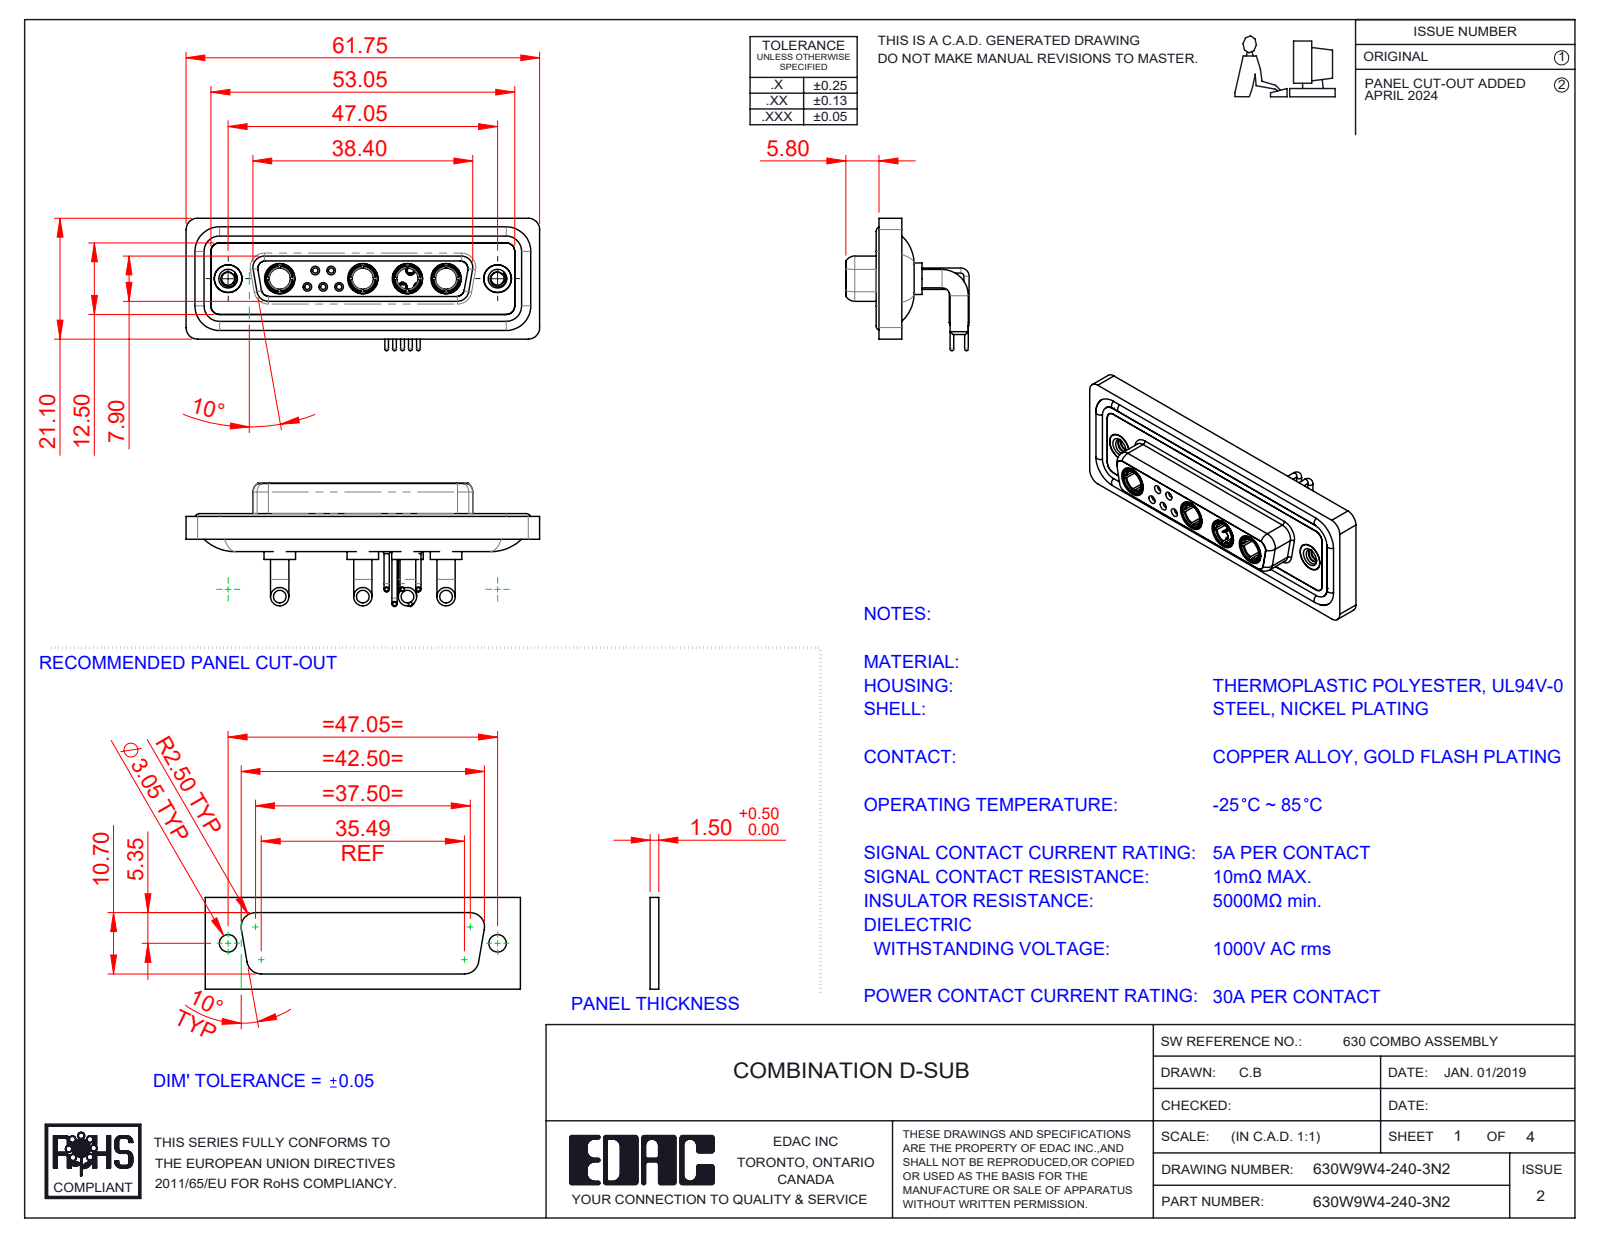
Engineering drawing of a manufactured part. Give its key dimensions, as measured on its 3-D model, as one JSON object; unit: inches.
{"part_name": "630W9W4-240-3N2; 630Combo Housing_9W4; 630Combo Shell Front_25 Contacts; 630Combo Threaded Rivet_2 (+5 more)", "step_written_by": "SolidWorks 2023 (CONFIG_CONTROL_DESIGN)", "units": "inches", "bodies": {"solids": 20, "faces": 963, "planar": 296, "cylindrical": 403, "other": 264}, "overall_size": [2.431, 0.91, 0.848], "volume_in3": 0.523, "surface_area_in2": 21.89, "round_holes": [[0.191, 6], [0.035, 5], [0.043, 5], [0.059, 5], [0.079, 5], [0.146, 4], [0.209, 4], [0.063, 3], [0.067, 2], [0.089, 2], [0.157, 2], [0.159, 2]], "round_bosses_or_shafts": [[0.035, 10], [0.063, 9], [0.126, 8], [0.079, 5], [0.059, 5], [0.026, 5], [0.217, 4], [0.205, 4]], "partial_cylinders_radius": [[0.059, 18], [0.079, 18], [0.053, 8], [0.063, 8], [0.01, 4], [0.02, 4], [0.024, 4], [0.026, 4]], "face_to_face_distances": [0.016, 0.071, 0.161, 0.043, 0.063, 0.059, 0.098, 0.122, 0.146, 0.055], "hole_center_spacings": [0.124, 0.109, 0.198, 0.545, 0.436, 0.504, 0.61, 0.218]}
